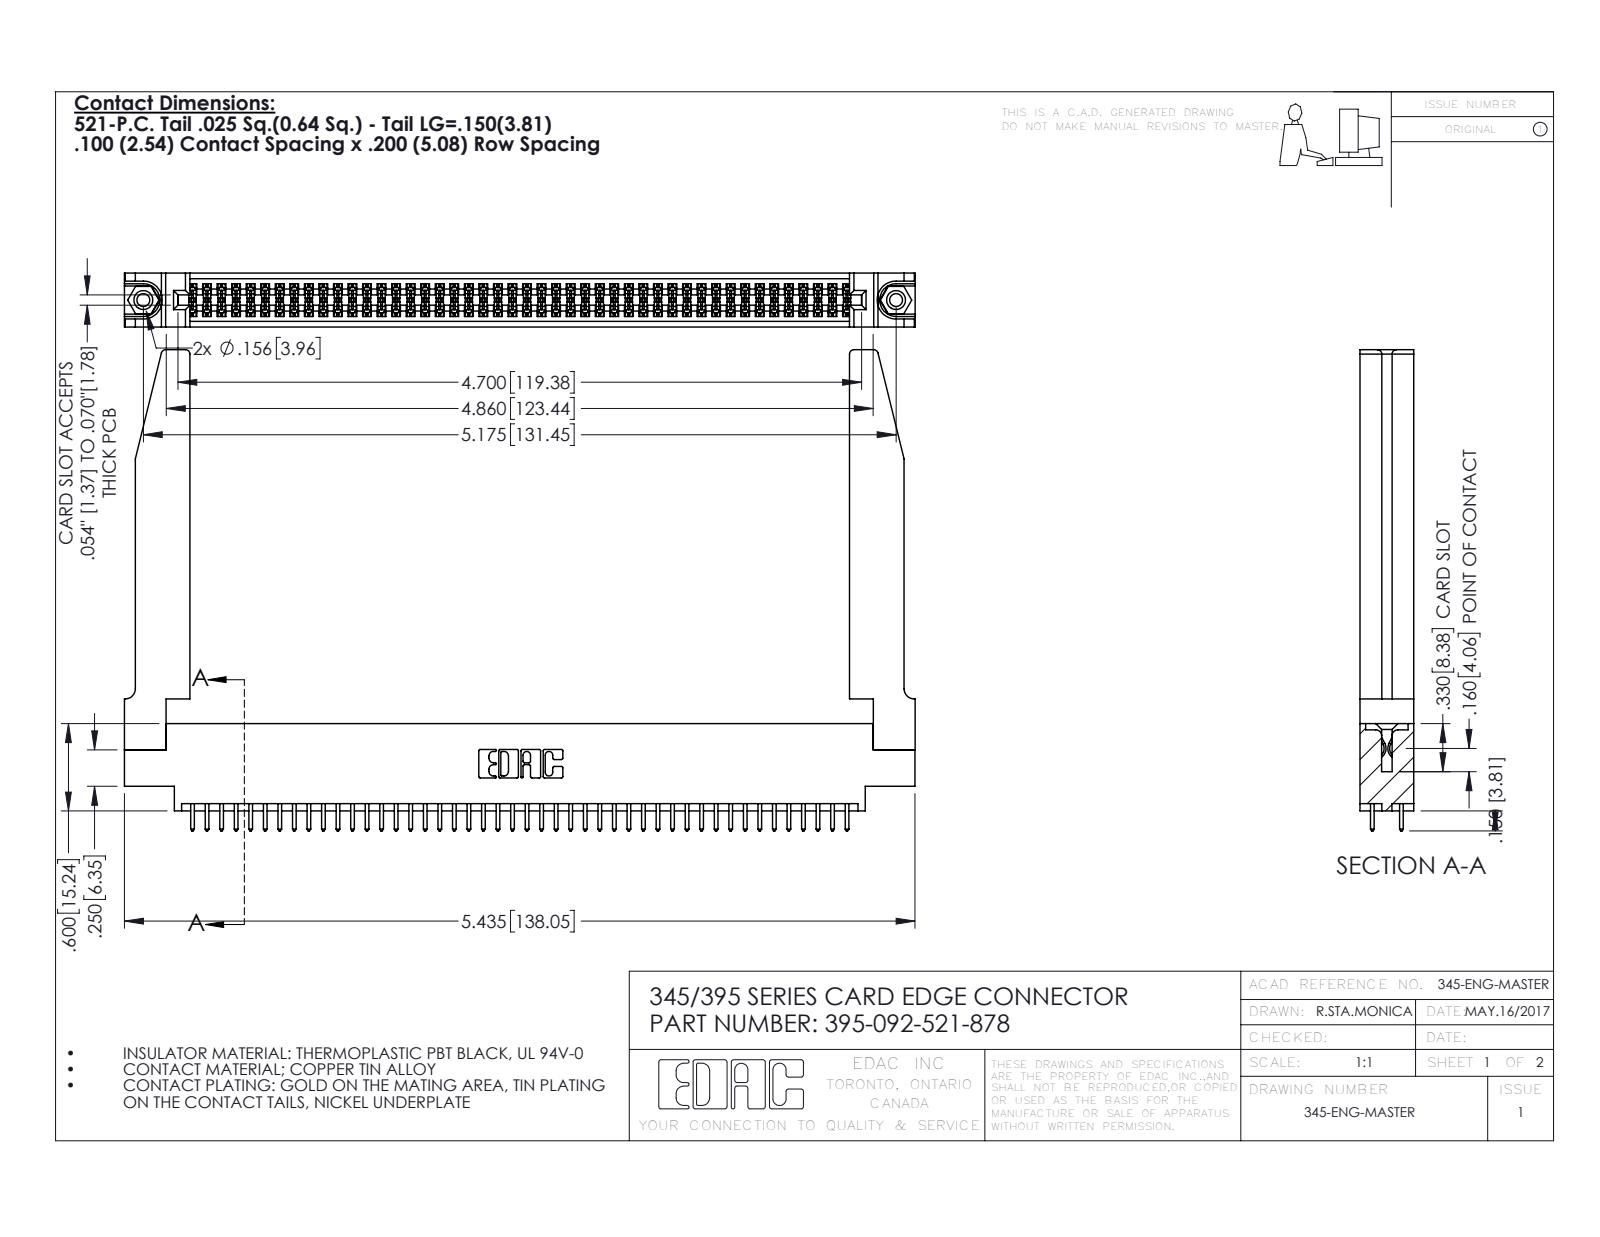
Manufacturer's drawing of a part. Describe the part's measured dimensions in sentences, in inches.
The part is named "345-250-001_345-250-001-102; 345 Part_0.170 Offset - 0.156 Dia-TH; 395-092-521-878; 345-220-078_345-220-078 (+1 more)". Its 3-D file was written by "SolidWorks 2016 (CONFIG_CONTROL_DESIGN)". It is 97 solids with 4964 faces: 3262 planar, 1650 cylindrical and 52 other. Overall it measures 5.436 by 3.307 by 0.37 inches. Its volume is 1.286 cubic inches and its surface area 41.03 square inches. Round holes: 2 of diameter 0.089, 2 of diameter 0.125, 2 of diameter 0.156, 1 of diameter 0.064. Round bosses or shafts: 2 of diameter 0.155. Partial cylindrical surfaces (rounded edges, fillets, slot ends): 138 of radius 0.006, 92 of radius 0.01, 22 of radius 0.01, 8 of radius 0.03, 6 of radius 0.007, 6 of radius 0.031, 3 of radius 0.026, 2 of radius 0.014. The main face-to-face distances are 0.072, 0.37, 0.298, 0.2, 0.098, 0.272, 0.025, 0.225, 0.175, 0.148. The hole center spacings are 0.27, 4.939, 5.175.
